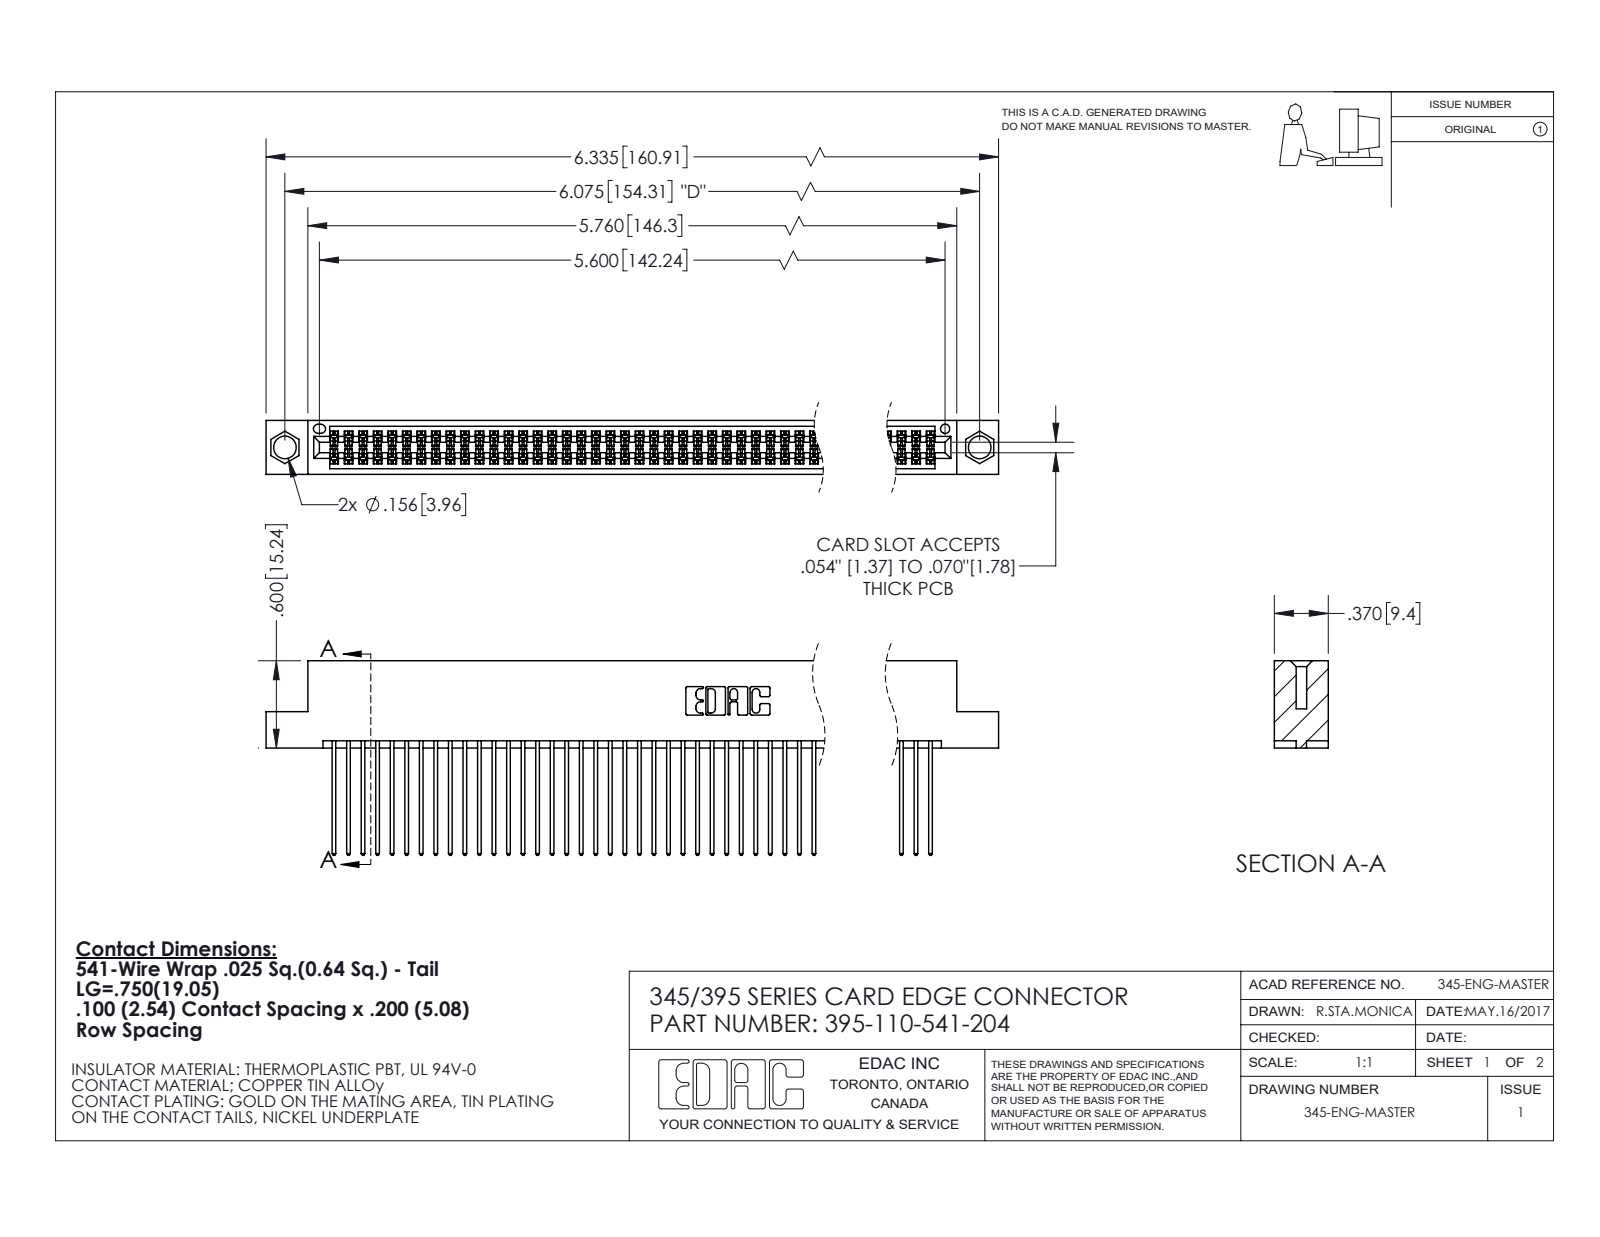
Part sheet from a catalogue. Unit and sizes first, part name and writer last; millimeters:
Units: millimetres
Overall size (bounding box): 160.9 × 34 × 9.4
Round holes (diameter × count): ⌀4 ×2, ⌀1.6 ×1
Partial cylindrical surfaces — rounded edges, fillets, slot ends (radius × count): R0.2 ×220, R0.3 ×110, R0.3 ×22, R0.2 ×6, R0.8 ×6, R0.7 ×3, R0.4 ×2, R0.5 ×2
Main face-to-face distances: 7.6, 1.8, 5.1, 2.5, 6.9, 0.6, 5.7, 9.4, 4.4, 3.8
Hole centre spacings: 6.9, 148.3, 154.3
Volume: 16 300 mm³ · Surface area: 27 130 mm²
Bodies: 111 solids, 5640 faces (3724 planar, 1916 cylindrical, 0 other)
Part name (STEP PRODUCT): 395-110-541-204; 345-292-001_345-293-141; 345 Part_Flush Mounting Lugs - 0.156 Dia-TI
STEP written by: SolidWorks 2020 (CONFIG_CONTROL_DESIGN)
